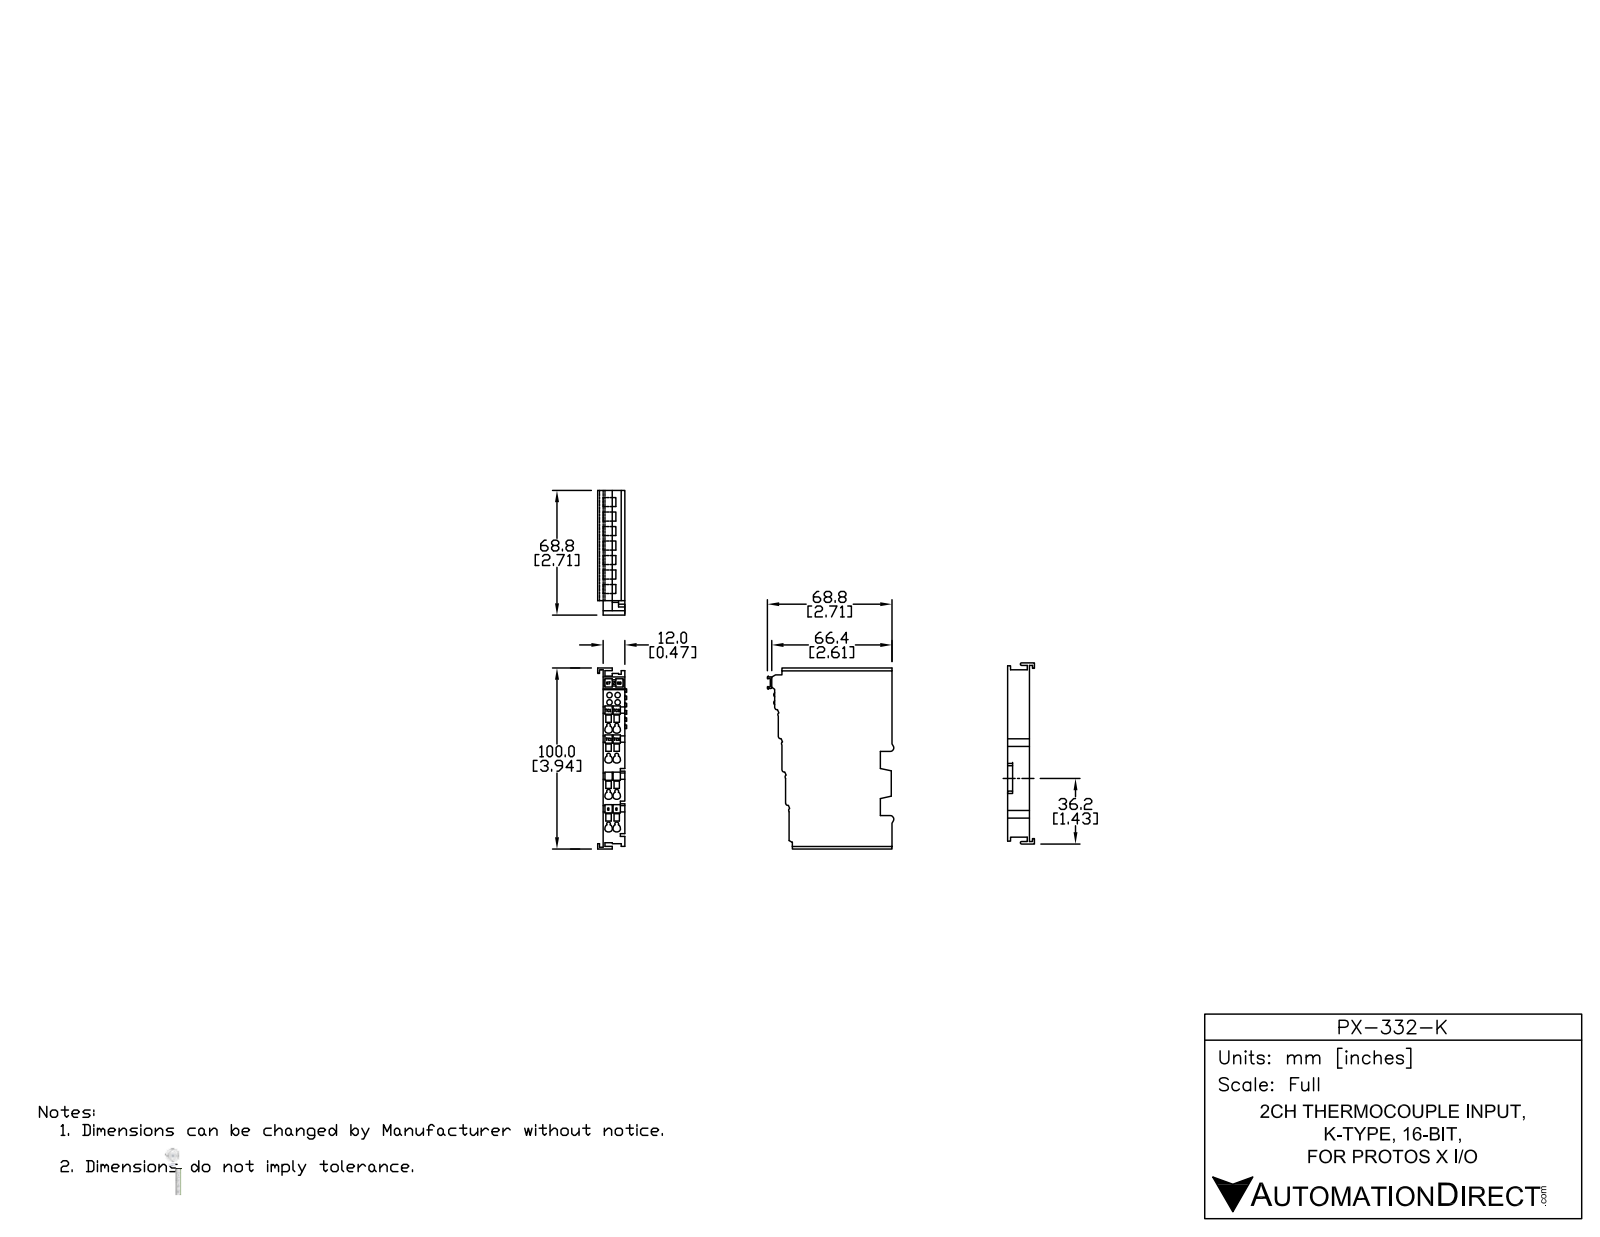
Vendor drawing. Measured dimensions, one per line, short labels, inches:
name: PX-332-K
written by: SolidWorks 2014 (AUTOMOTIVE_DESIGN)
unit: in
bodies: 28 solids, 1367 faces (963 planar, 344 cylindrical, 60 other)
size: 3.947 × 2.806 × 0.596
volume: 3.564 in³; area: 52.52 in²
holes: 8× ⌀0.157, 4× ⌀0.138
rounds: 46× R0.012, 35× R0.01, 12× R0.015, 10× R0.005, 9× R0.039, 8× R0.016, 4× R0.007, 4× R0.041
face distances: 0.472, 0.039, 0.079, 0.394, 0.073, 0.433, 0.343, 0.157, 0.124, 0.048
hole spacings: 0.177, 0.197, 0.724, 0.751, 0.25, 0.63, 0.66, 0.804
